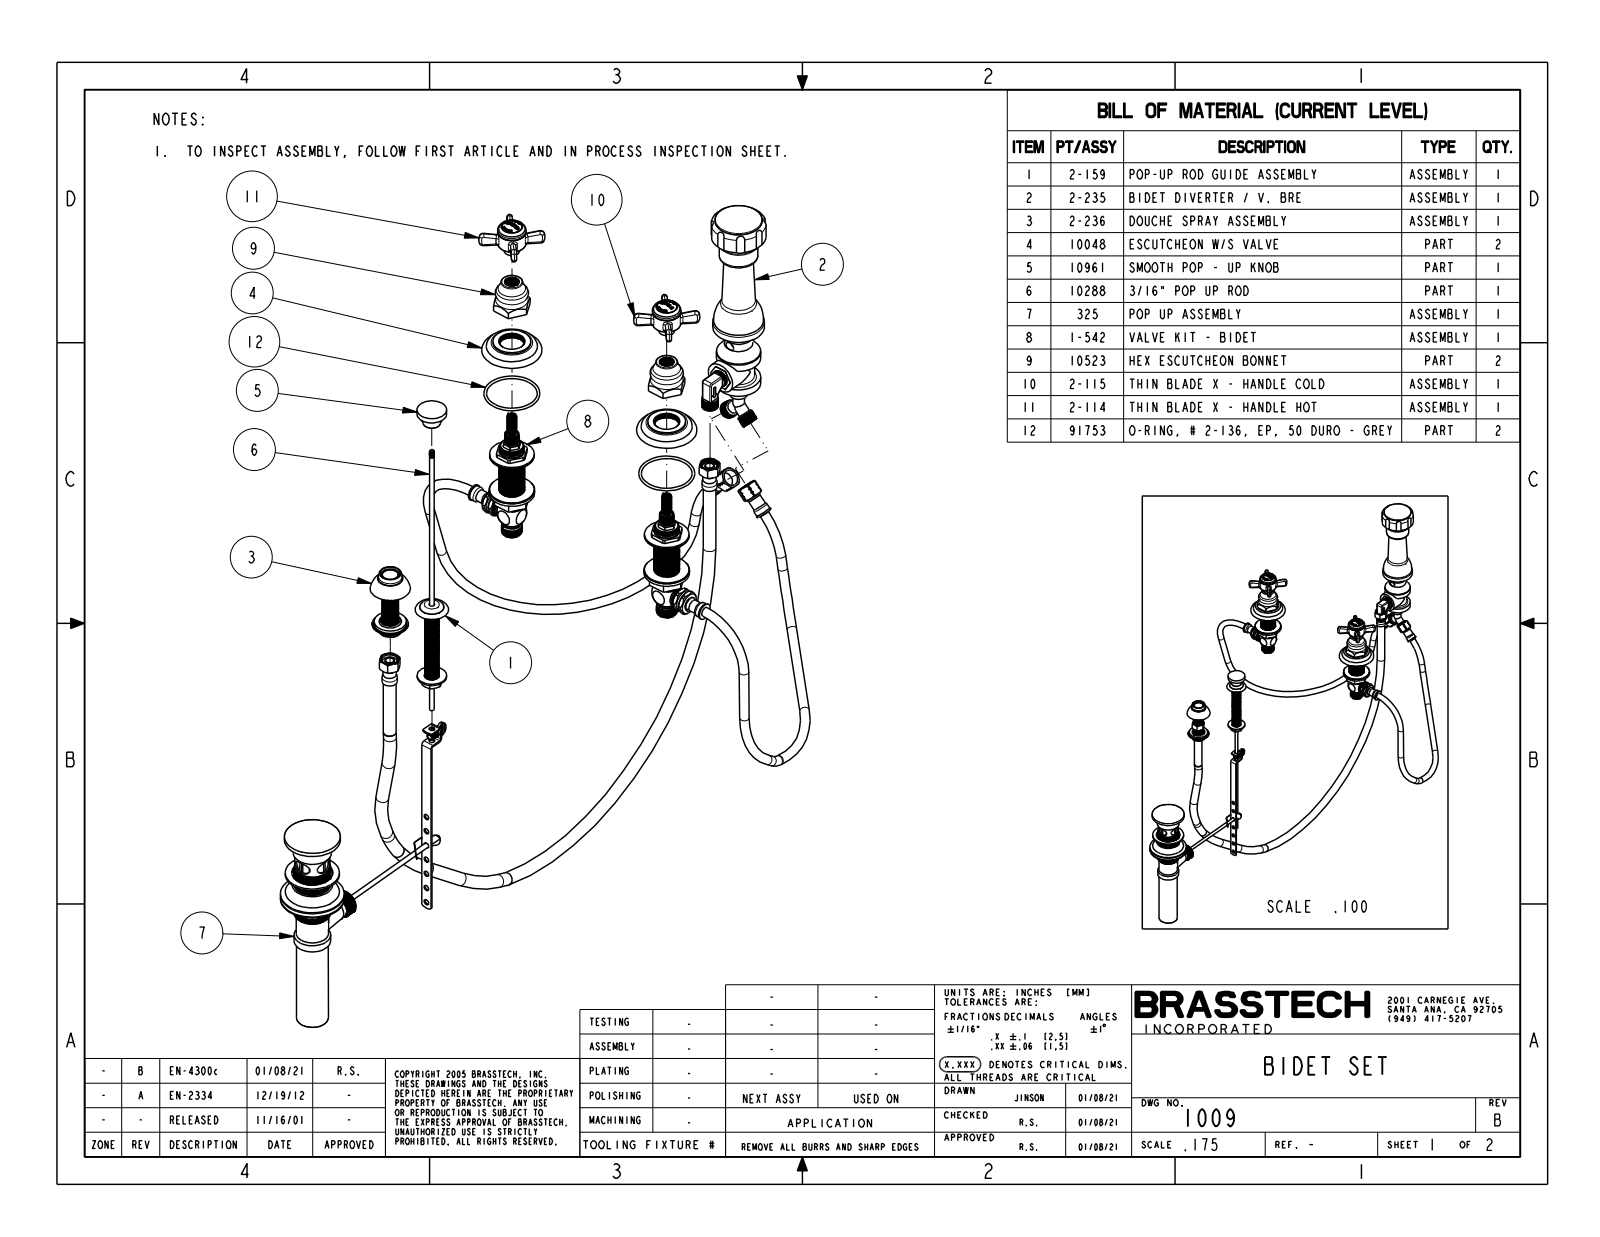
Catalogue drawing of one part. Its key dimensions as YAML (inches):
part_name: "1009"
step_written_by: "CREO PARAMETRIC BY PTC INC, 2018400 (CONFIG_CONTROL_DESIGN)"
units: inches
bodies: {solids: 5, faces: 1125, planar: 475, cylindrical: 344, other: 306}
overall_size: [22.855, 10.36, 5.353]
volume: 20.63
surface_area: 96.45
round_holes:
  - {diameter: 0.815, count: 2}
  - {diameter: 0.625, count: 1}
  - {diameter: 0.792, count: 1}
  - {diameter: 0.94, count: 1}
round_bosses_or_shafts:
  - {diameter: 1.482, count: 2}
  - {diameter: 1.115, count: 2}
  - {diameter: 1.1, count: 2}
  - {diameter: 0.99, count: 2}
  - {diameter: 0.8, count: 2}
  - {diameter: 0.603, count: 2}
  - {diameter: 2.025, count: 1}
  - {diameter: 1.52, count: 1}
partial_cylinders:
  - {radius: 0.011, count: 28}
  - {radius: 0.1, count: 25}
  - {radius: 0.025, count: 17}
  - {radius: 0.006, count: 14}
  - {radius: 0.005, count: 10}
  - {radius: 0.015, count: 10}
  - {radius: 0.006, count: 8}
  - {radius: 0.014, count: 8}
face_to_face_distances: [0.2, 5.656, 2.037, 6.928, 1.313, 5.456, 5.856, 0.375, 1.662, 3.468]
hole_center_spacings: [12.649, 8]
